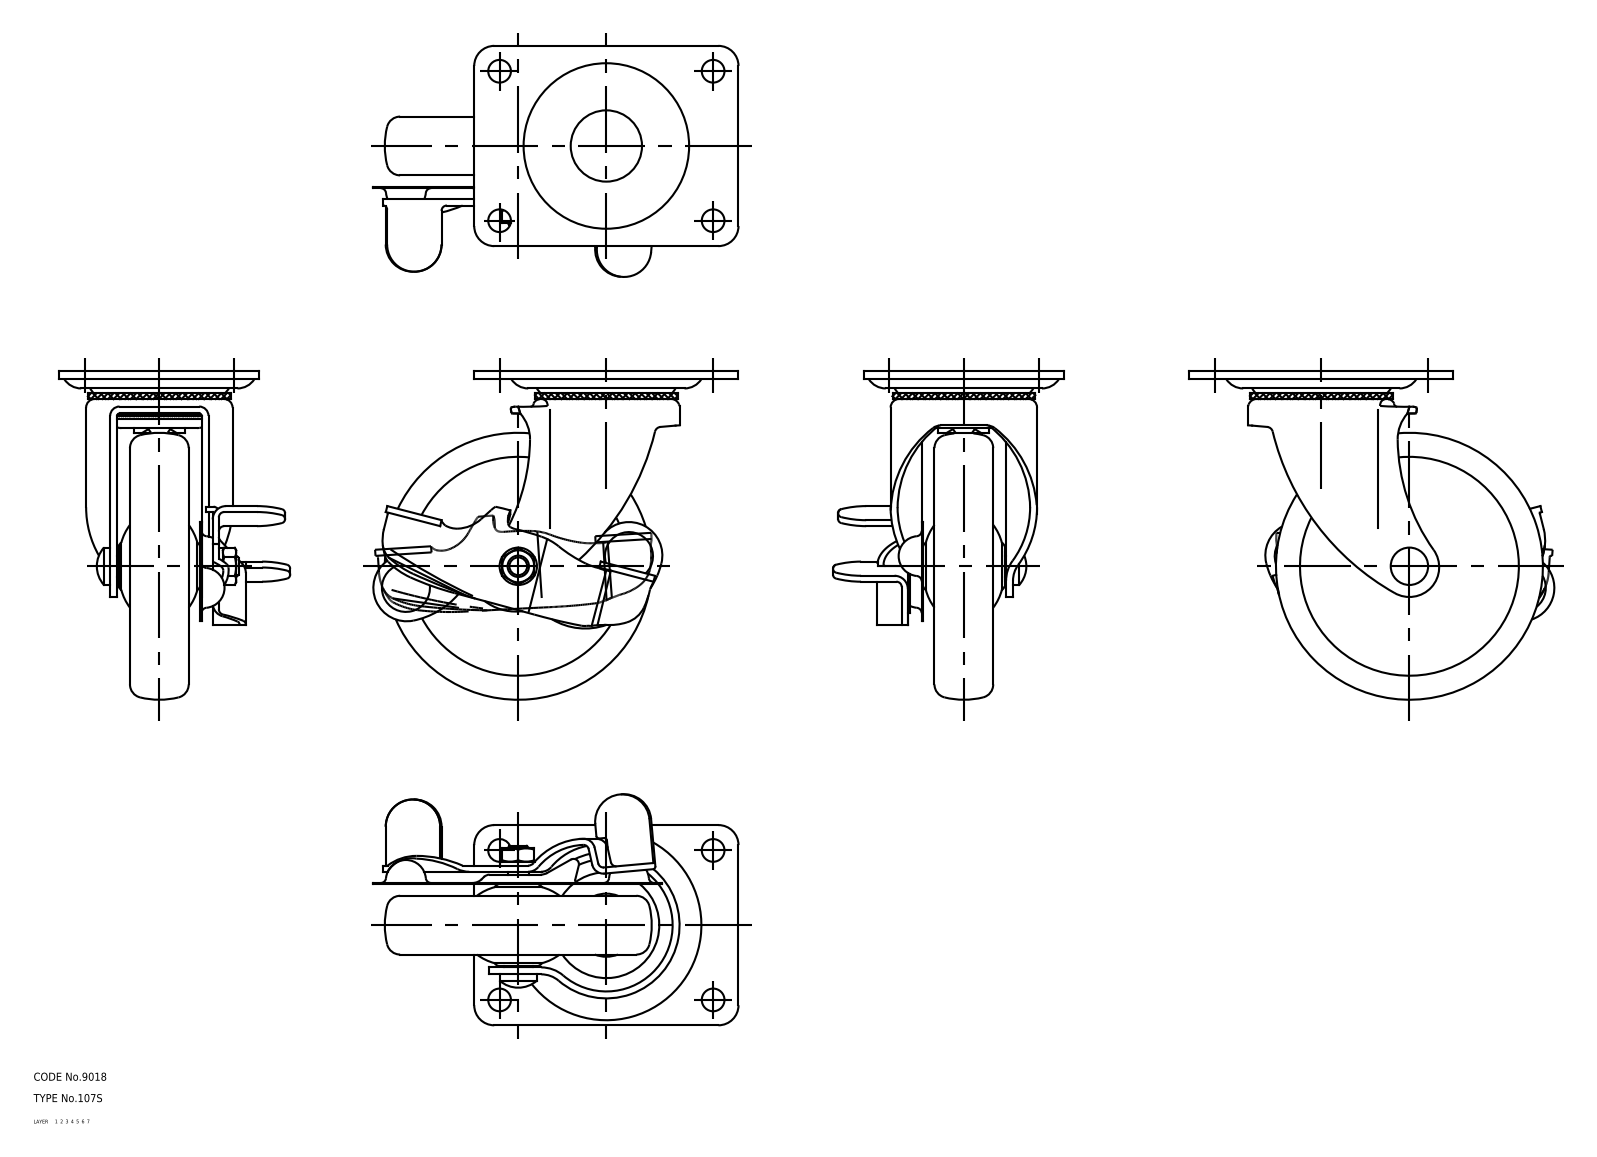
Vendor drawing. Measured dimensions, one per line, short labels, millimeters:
name: wheel; plate; mounting plate; main shaft (+3 more)
written by: CADfix (AUTOMOTIVE_DESIGN)
unit: mm
bodies: 7 solids, 374 faces (0 planar, 0 cylindrical, 374 other)
size: 136.79 × 123 × 86.62
volume: 214 972 mm³; area: 80 827 mm²
